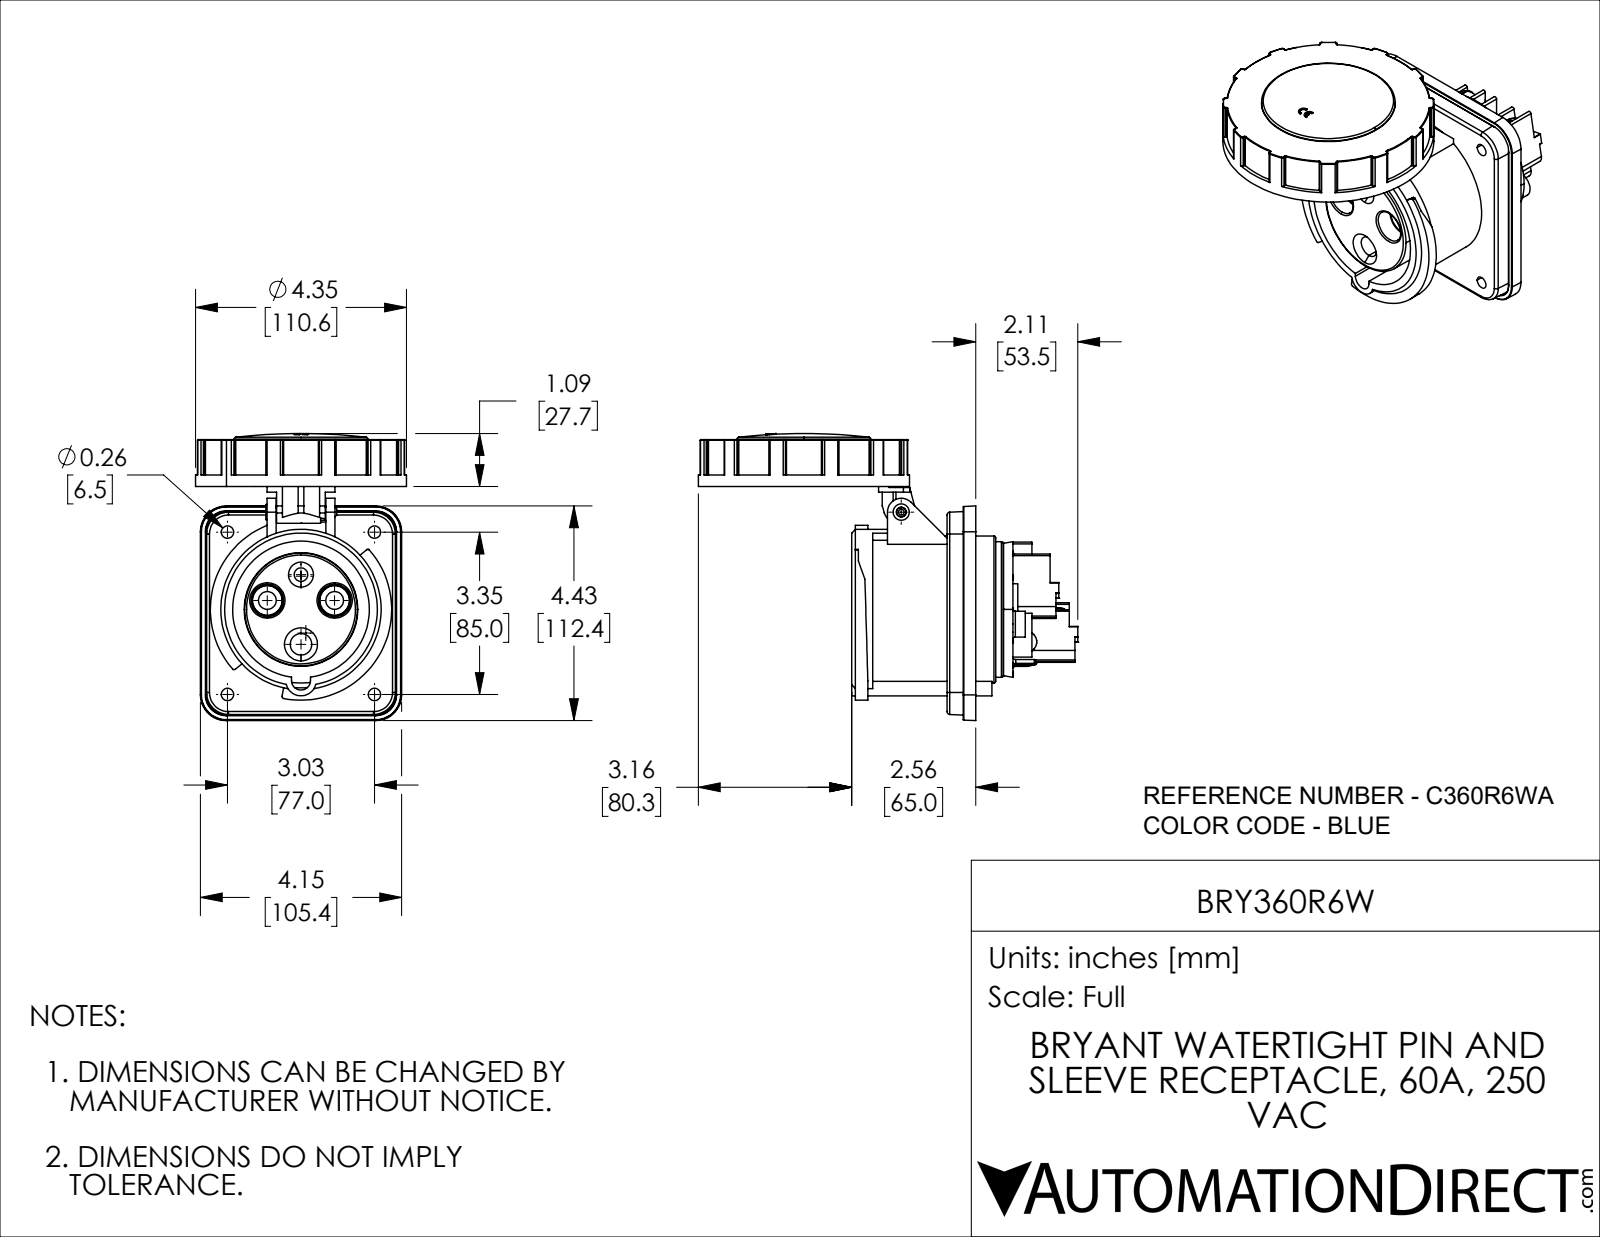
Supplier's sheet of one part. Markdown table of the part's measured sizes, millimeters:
| quantity | value |
| --- | --- |
| part name | BRY360R6W |
| STEP written by | SolidWorks 2021 (CONFIG_CONTROL_DESIGN) |
| units | millimeters |
| bodies | 2 solids, 1659 faces (667 planar, 576 cylindrical, 416 other) |
| overall size | 198.78 × 150.35 × 110.55 |
| volume | 639 602 mm³ |
| surface area | 131 425 mm² |
| round holes (diameter × count) | 5.8 × 6, 6.5 × 4, 9 × 2, 9.3 × 2, 3 × 1, 3.6 × 1, 5 × 1, 5.1 × 1, 7.1 × 1, 8.5 × 1, 11.3 × 1, 71.6 × 1 |
| round bosses / shafts (diameter × count) | 5 × 7, 5.75 × 6, 110.55 × 1, 84 × 1, 77 × 1, 71 × 1, 70 × 1, 69.24 × 1 |
| partial cylindrical surfaces (radius × count) | 0.5 × 61, 0.3 × 48, 1 × 34, 0.25 × 20, 0.2 × 12, 2 × 7, 4.5 × 7, 1.01 × 6 |
| main face-to-face distances | 15, 63, 19.5, 48, 2, 11, 24.5, 6.5, 58.5, 82.5 |
| hole center spacings | 18.25, 9, 17.11, 18.33, 21.75, 22.22, 23.89, 28.96 |
